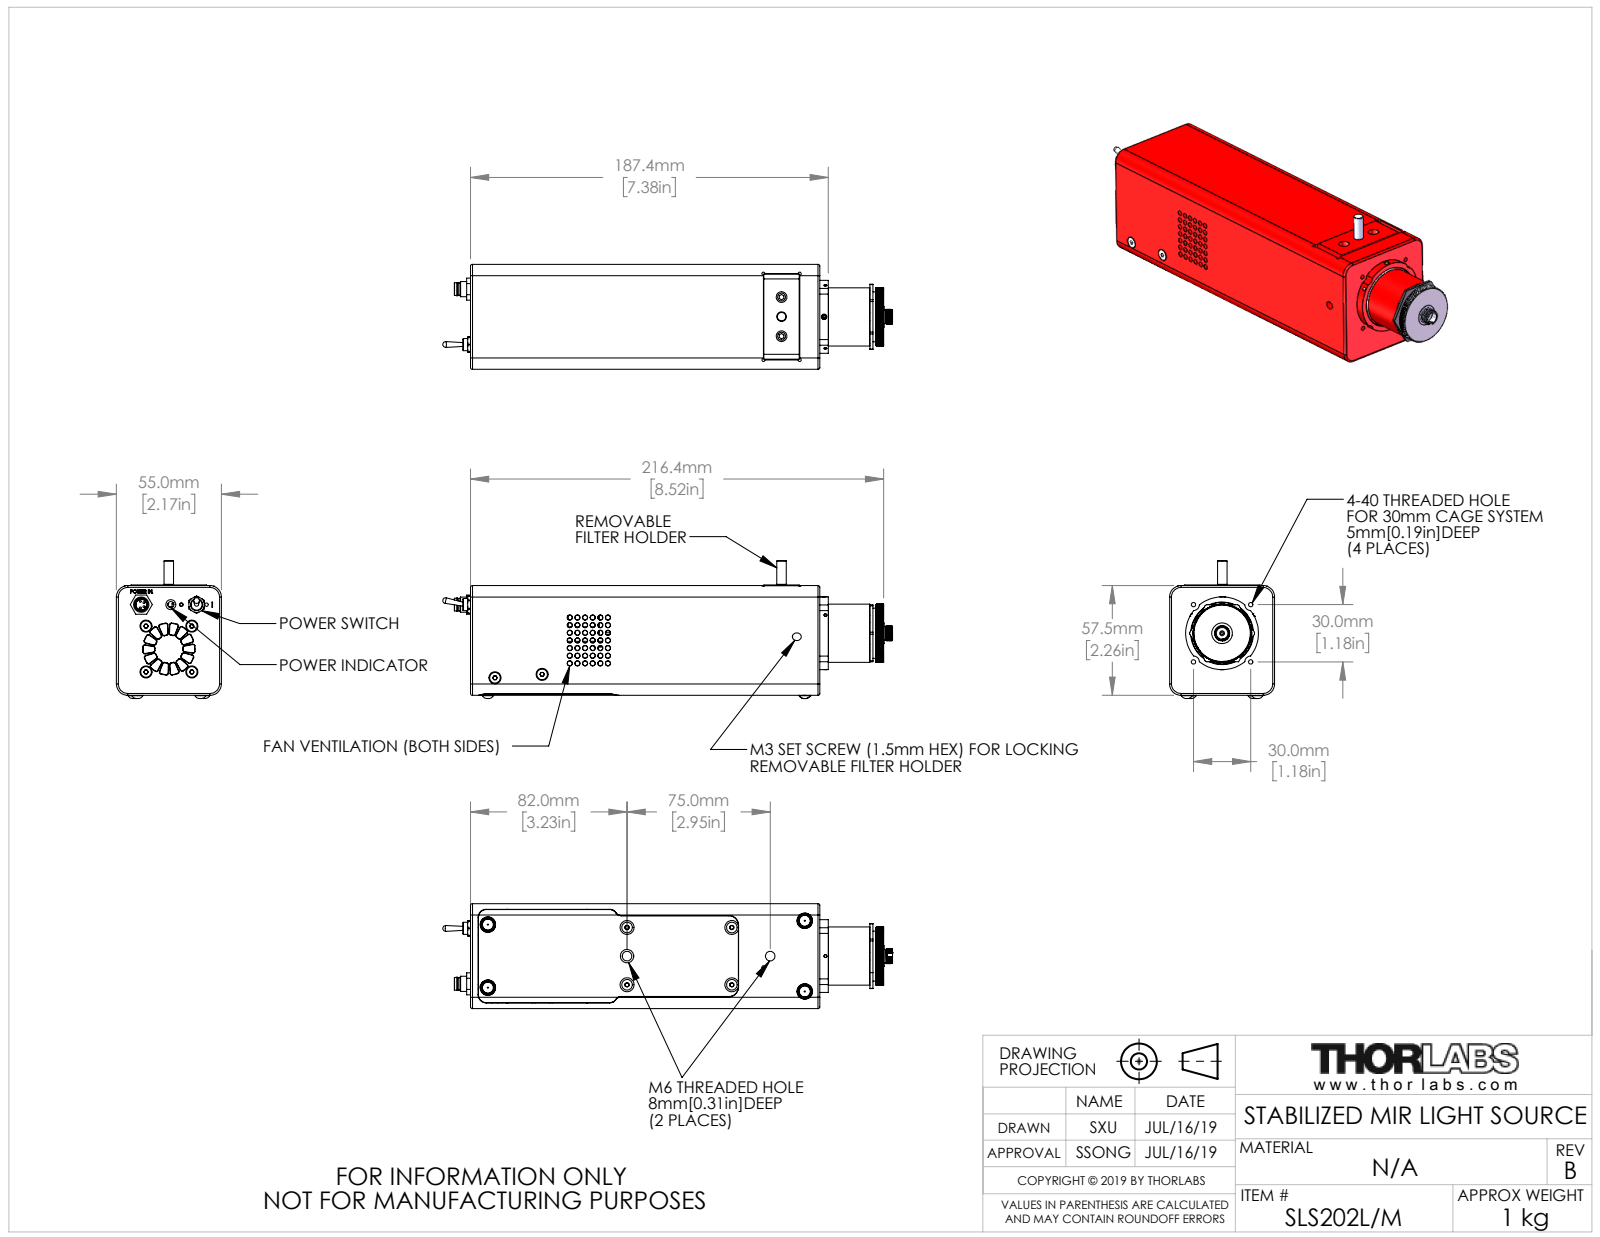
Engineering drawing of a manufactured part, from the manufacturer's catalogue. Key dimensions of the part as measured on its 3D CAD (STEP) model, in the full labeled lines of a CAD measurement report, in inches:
Part name (STEP PRODUCT): BULB HOLDER BASE ASSY; bulb module; LB5774-Solidworks; dowel pin 1.8x4 (+8 more)
STEP written by: SolidWorks 2018 (CONFIG_CONTROL_DESIGN)
Units: inches
Bodies: 86 solids, 4180 faces (1670 planar, 1298 cylindrical, 1212 other)
Overall size (bounding box): 9.276 × 2.845 × 2.165
Volume: 19.68 in³ · Surface area: 227.4 in²
Round holes (diameter × count): ⌀0.098 ×59, ⌀0.063 ×10, ⌀0.134 ×10, ⌀0.024 ×6, ⌀0.039 ×6, ⌀0.059 ×6, ⌀0.126 ×6, ⌀0.094 ×5, ⌀0.089 ×4, ⌀0.102 ×4, ⌀0.122 ×4, ⌀0.138 ×4
Round bosses / shafts (diameter × count): ⌀0.118 ×21, ⌀0.218 ×10, ⌀0.079 ×9, ⌀0.059 ×7, ⌀0.04 ×7, ⌀0.217 ×6, ⌀0.018 ×6, ⌀0.276 ×5
Partial cylindrical surfaces — rounded edges, fillets, slot ends (radius × count): R0.031 ×60, R0.039 ×33, R0.079 ×29, R0.016 ×16, R0.118 ×11, R0.157 ×9, R0.063 ×7, R0.063 ×7
Main face-to-face distances: 0.118, 2.165, 2.264, 0.197, 2.047, 2.067, 0.063, 0.654, 0.394, 1.929
Hole centre spacings: 0.071, 1.181, 0.157, 0.449, 0.495, 0.224, 0.315, 0.945
